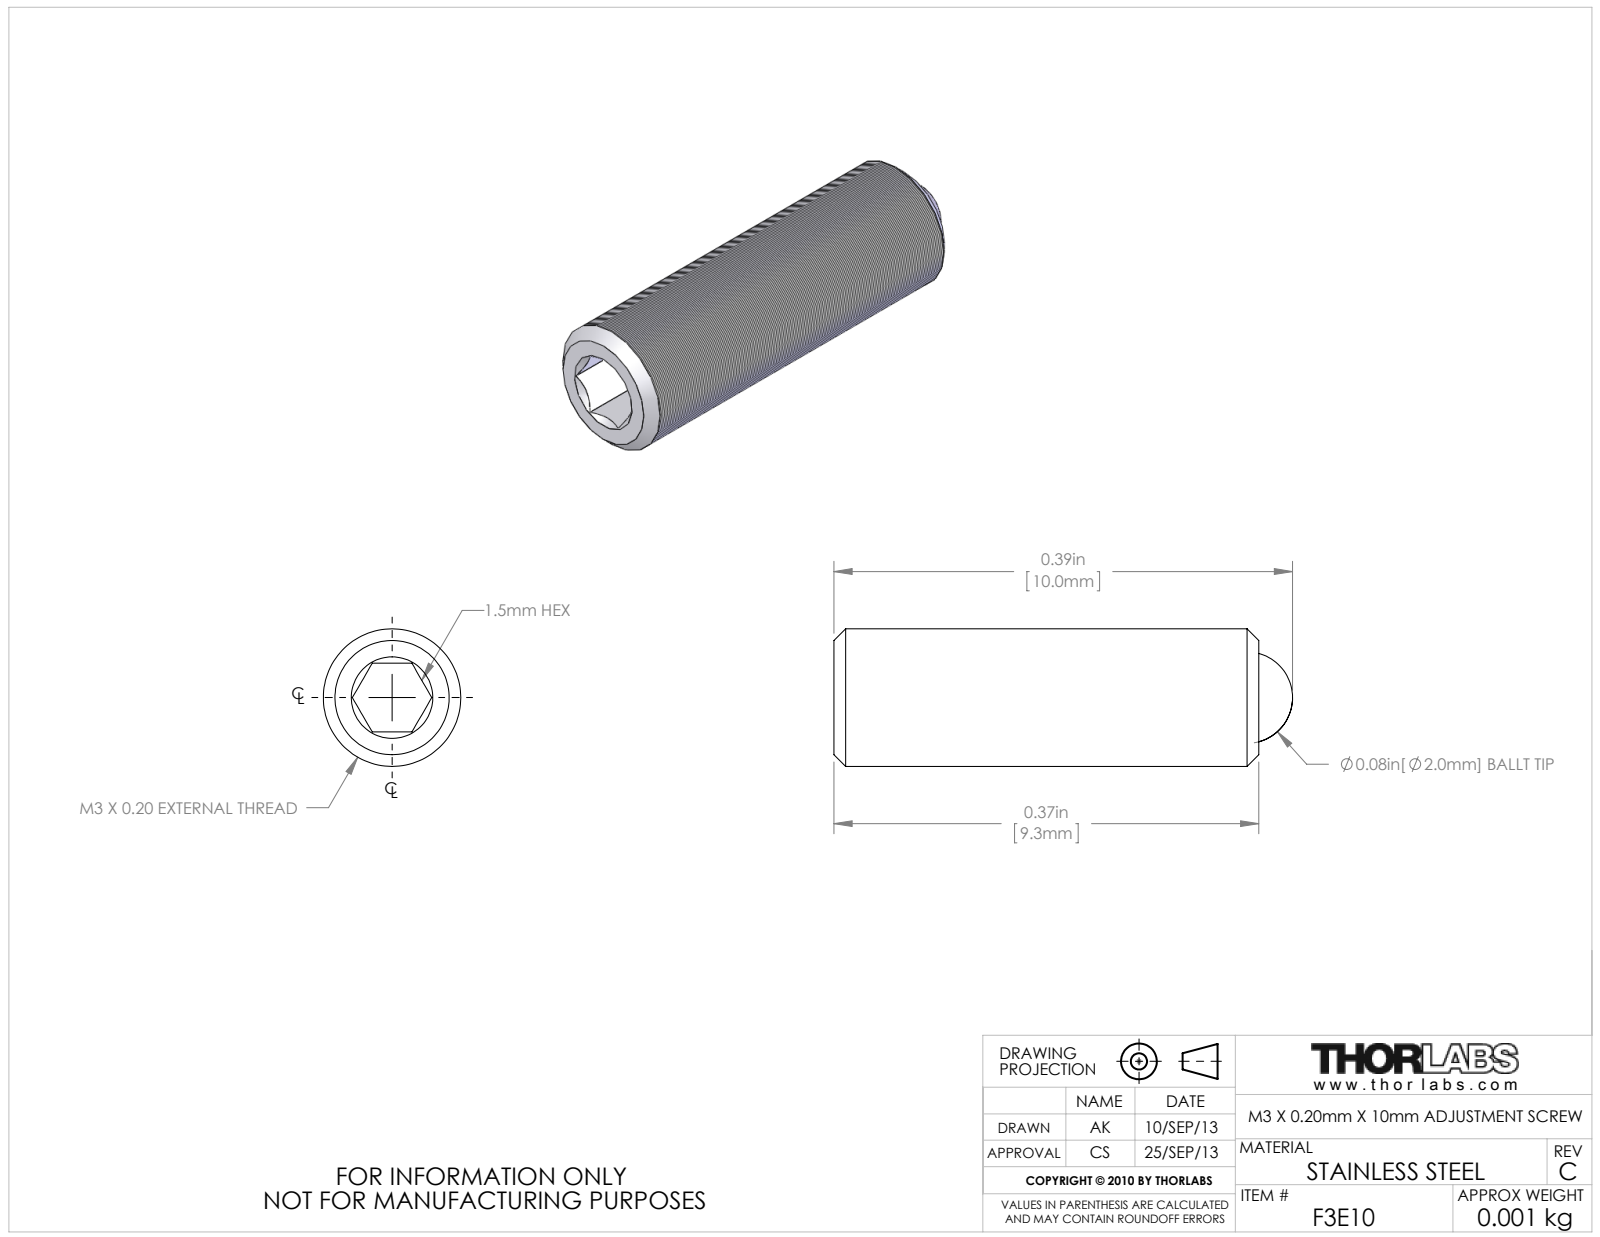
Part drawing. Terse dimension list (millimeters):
name: 8564-E0W
written by: SolidWorks 2012 (AUTOMOTIVE_DESIGN)
unit: mm
bodies: 2 solids, 25 faces (9 planar, 4 cylindrical, 12 other)
size: 10 × 3 × 3
volume: 70 mm³; area: 132 mm²
holes: 1× ⌀2
bosses: 1× ⌀3
face distances: 1.5, 3, 6.2, 9.3
